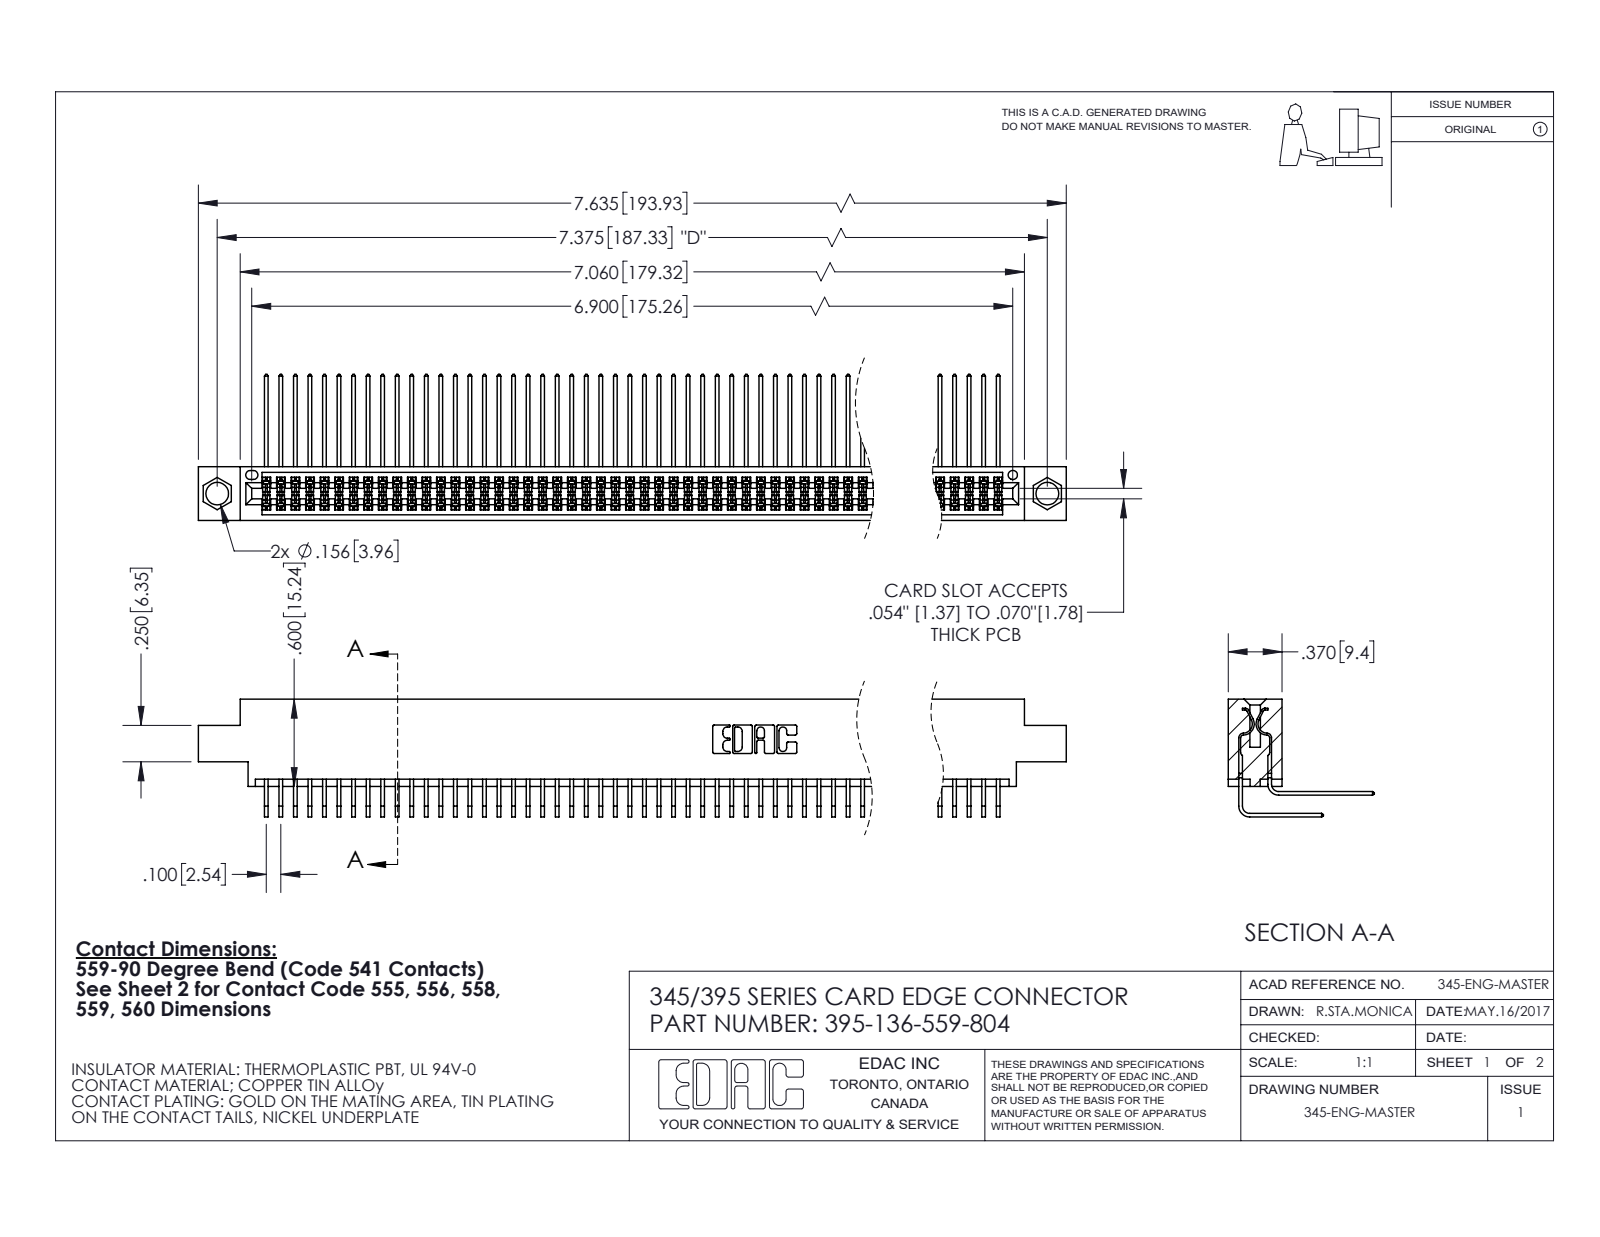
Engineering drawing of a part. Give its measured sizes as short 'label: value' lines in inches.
name: 345-292-001_558 559 Tail - 1; 395-136-559-804; 345 Part_0.170 Offset - 0.156 Dia-TI; 345-292-001_559 Tail - 2
written by: SolidWorks 2020 (CONFIG_CONTROL_DESIGN)
unit: in
bodies: 137 solids, 7216 faces (4858 planar, 2358 cylindrical, 0 other)
size: 7.635 × 1.005 × 0.809
volume: 1.199 in³; area: 51.5 in²
holes: 2× ⌀0.156, 1× ⌀0.064
rounds: 204× R0.006, 22× R0.01, 6× R0.007, 6× R0.031, 3× R0.026, 2× R0.014, 2× R0.019, 2× R0.022
face distances: 0.072, 0.298, 0.37, 0.2, 0.098, 0.272, 0.025, 0.225, 0.175, 0.15
hole spacings: 0.27, 7.139, 7.375
